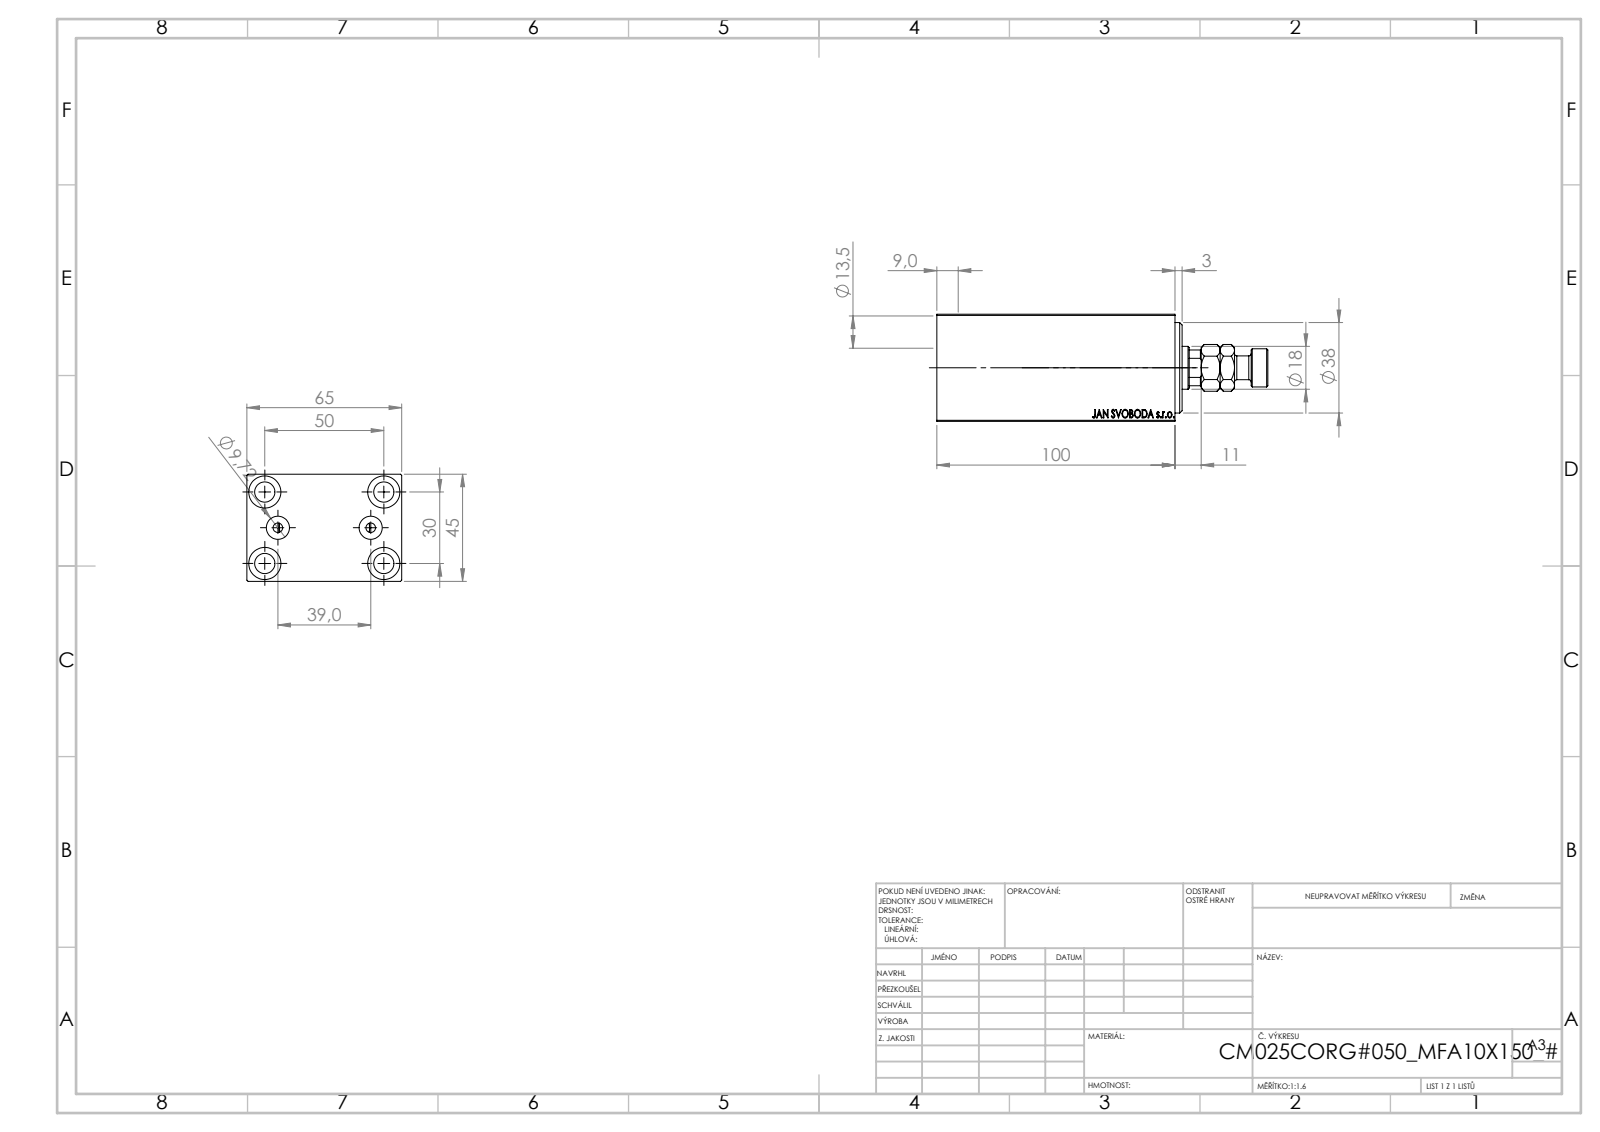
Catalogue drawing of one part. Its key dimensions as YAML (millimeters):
part_name: "V450CM_C_Body; V450CM_C_VCP; V450CM_VC_B; MFA"
step_written_by: "SolidWorks 2019 (CONFIG_CONTROL_DESIGN)"
units: millimeters
bodies: {solids: 4, faces: 910, planar: 424, cylindrical: 60, other: 426}
overall_size: [139, 65, 45]
volume: 257497
surface_area: 63560
round_holes:
  - {diameter: 8.5, count: 5}
  - {diameter: 13.5, count: 4}
  - {diameter: 4, count: 2}
  - {diameter: 9.72, count: 2}
  - {diameter: 18, count: 1}
  - {diameter: 21.5, count: 1}
  - {diameter: 25, count: 1}
  - {diameter: 27, count: 1}
  - {diameter: 38, count: 1}
round_bosses_or_shafts:
  - {diameter: 16, count: 1}
  - {diameter: 10, count: 1}
partial_cylinders:
  - {radius: 8.5, count: 1}
face_to_face_distances: [45, 65, 6, 89, 94, 100, 95, 5, 3, 8]
hole_center_spacings: [15.98, 29.15, 46.96, 19.5, 30, 50, 58.31, 39]
